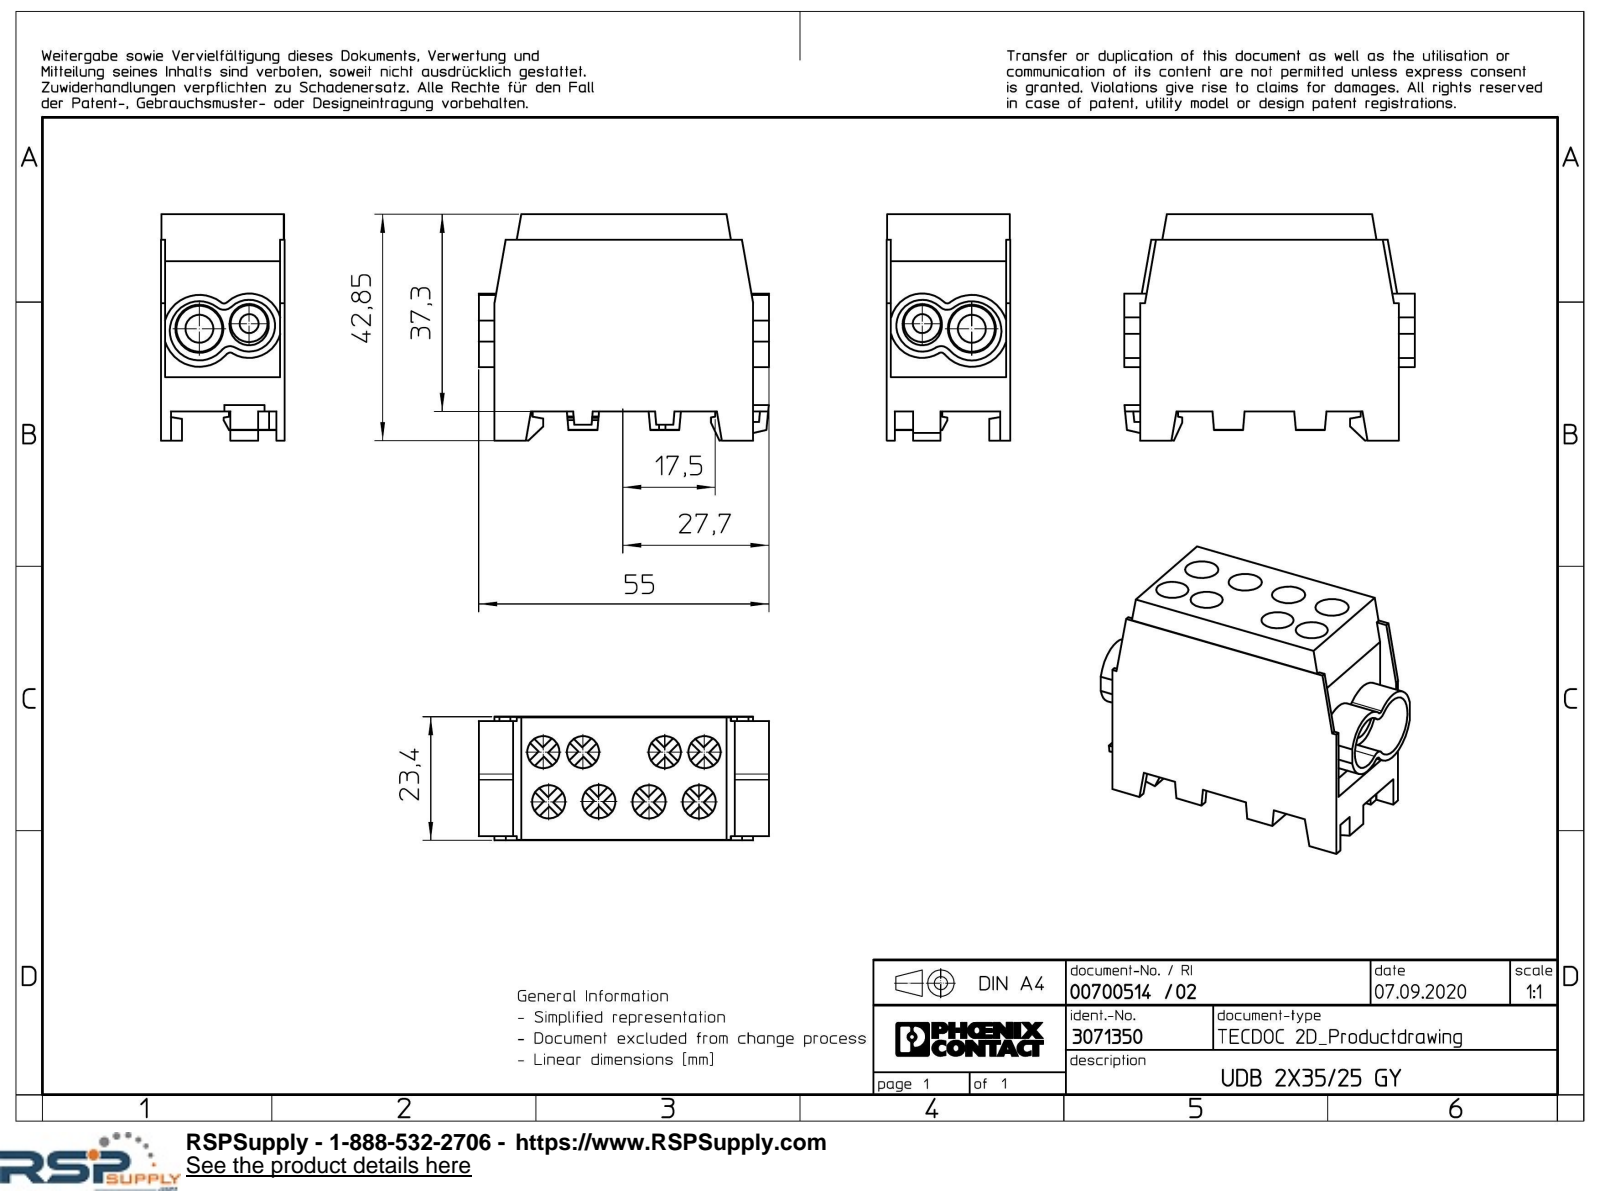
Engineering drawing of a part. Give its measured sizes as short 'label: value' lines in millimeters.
name: UDB_2x35_25_GY-select
written by: Creo Elements/Direct Modeling 20.1A 29-Sep-2018 (C) Parametric Technology GmbH (AUTOMOTIVE_DESIGN)
unit: mm
bodies: 1 solid, 275 faces (209 planar, 52 cylindrical, 14 other)
size: 55 × 42.85 × 23.4
volume: 33 975 mm³; area: 13 197 mm²
holes: 4× ⌀6.1, 4× ⌀6.3, 1× ⌀7, 1× ⌀8.7, 1× ⌀9.1
rounds: 2× R0.8, 2× R2, 2× R3.7, 1× R4.9, 1× R5.6, 1× R6.1, 1× R6.8
face distances: 23.4, 37.3, 3.5, 45.5, 23.3, 0.7, 0.8, 22.5, 6.5, 22.6
hole spacings: 9.45, 7.5, 11.43, 15.64, 22.1, 23, 23.92, 30.96
